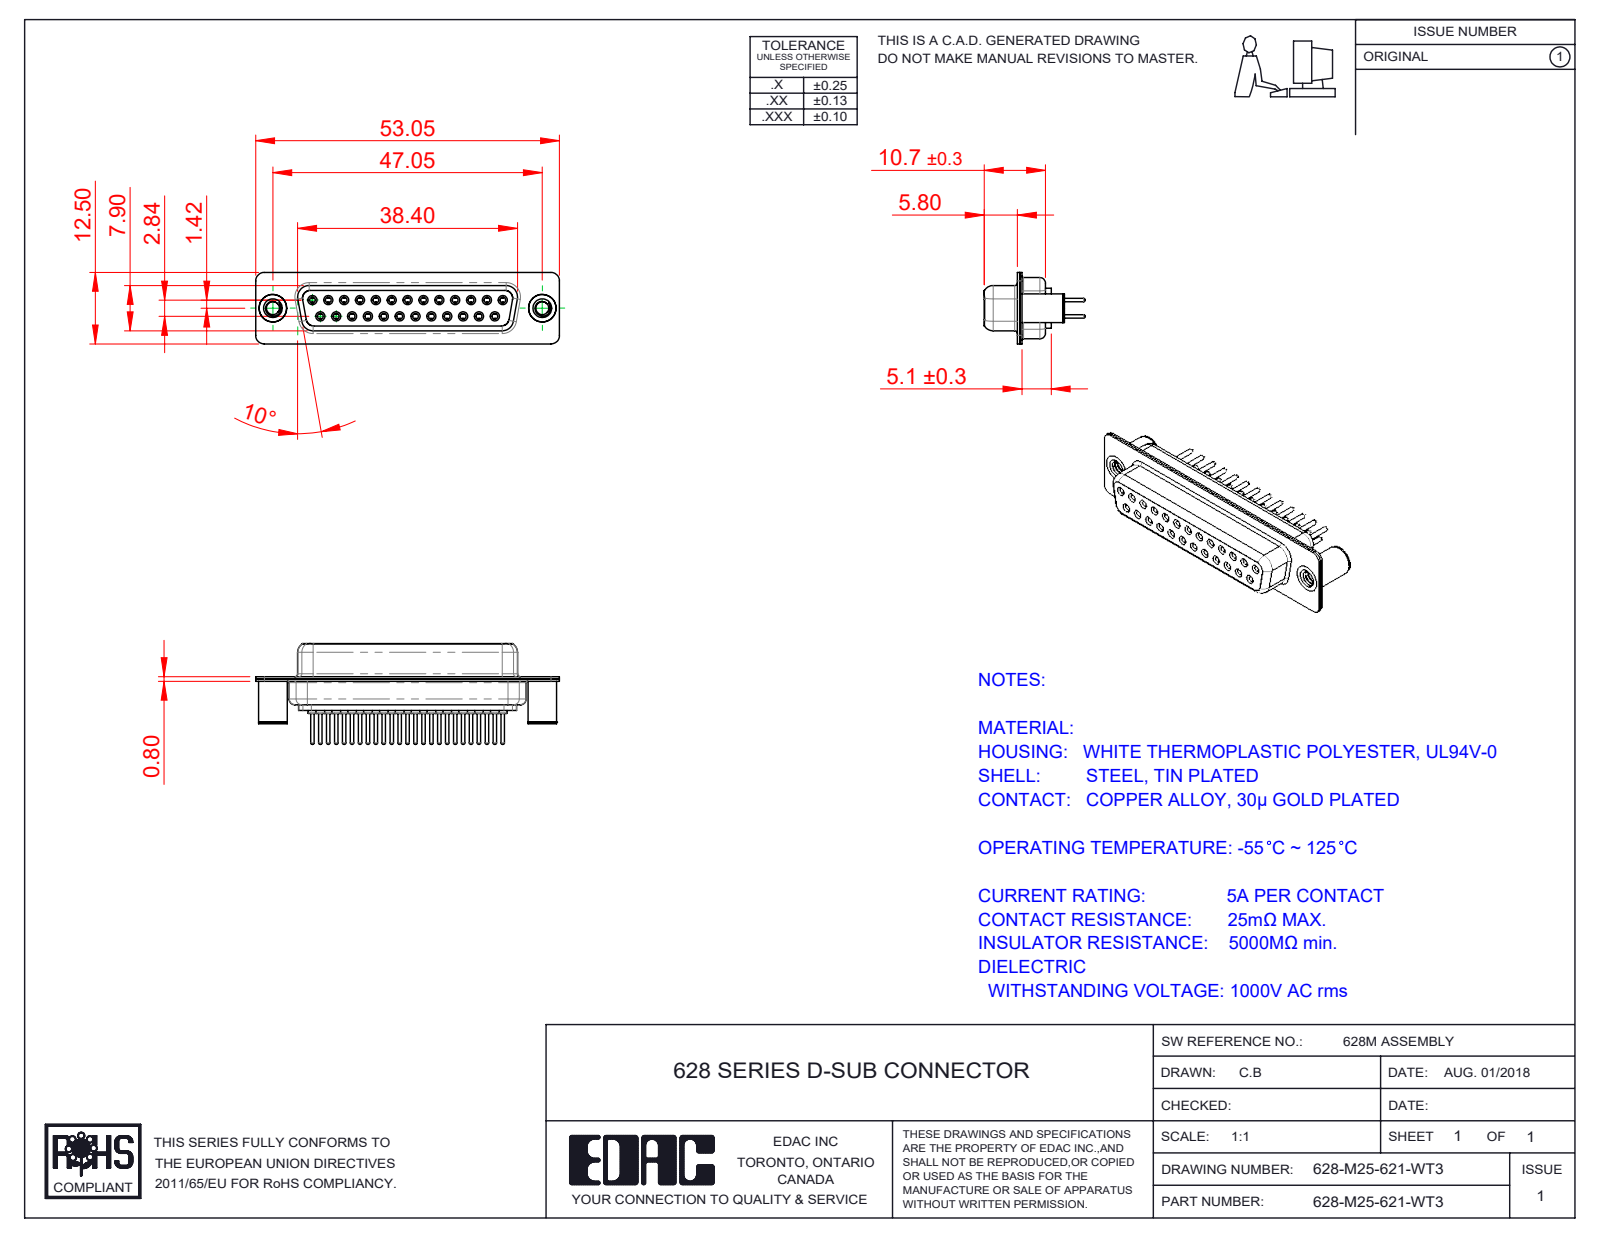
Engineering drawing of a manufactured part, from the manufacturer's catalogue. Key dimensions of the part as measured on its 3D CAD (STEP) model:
Part name (STEP PRODUCT): 628M Shell Rear_25 Contacts; 628M Shell Front_25 Contacts; 628M Housing_25 Contacts; 628M Contact Row 2_21 (+3 more)
STEP written by: SolidWorks 2020 (CONFIG_CONTROL_DESIGN)
Units: millimetres
Bodies: 30 solids, 1688 faces (442 planar, 636 cylindrical, 610 other)
Overall size (bounding box): 53.05 × 17.6 × 12.5
Volume: 3 863 mm³ · Surface area: 9 405 mm²
Round holes (diameter × count): ⌀1 ×25, ⌀1.1 ×25, ⌀1.7 ×25, ⌀1.8 ×25, ⌀2 ×25, ⌀2.26 ×2, ⌀3.26 ×2, ⌀4 ×2, ⌀4.8 ×2
Round bosses / shafts (diameter × count): ⌀2.2 ×25, ⌀1.6 ×25, ⌀1.5 ×25, ⌀0.6 ×25, ⌀5 ×2, ⌀4.9 ×2
Partial cylindrical surfaces — rounded edges, fillets, slot ends (radius × count): R1.5 ×16, R2 ×12, R1.35 ×8, R1.6 ×8, R0.25 ×4, R0.5 ×4, R0.6 ×4, R0.65 ×4
Main face-to-face distances: 0.4, 1.4, 0.45, 8.45, 8.9, 1.8, 6.2, 7.05, 1, 1.85
Hole centre spacings: 3.16, 2.77, 5.54, 8.31, 11.08, 13.85, 5.04, 7.49
